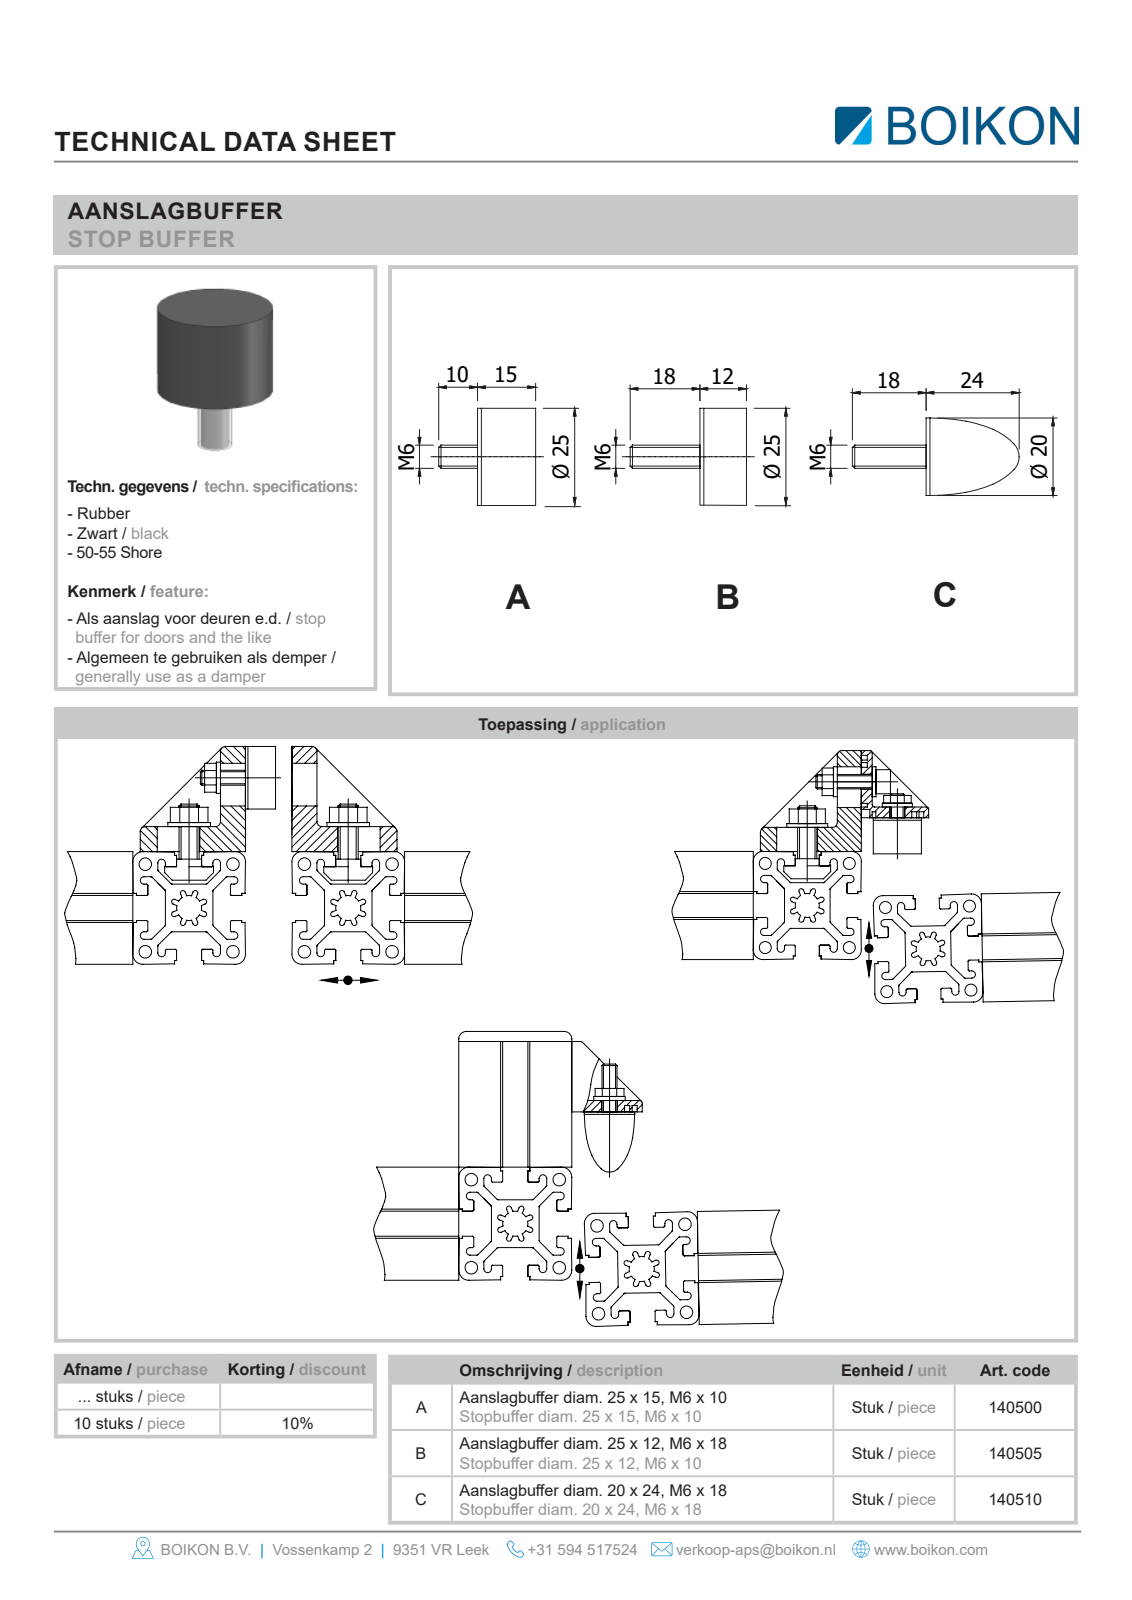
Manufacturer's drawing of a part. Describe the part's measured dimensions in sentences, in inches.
The part is named "Root; 140505Aanslagbuffer diam 25x12, M6x18BOIKON". Its 3-D file was written by "HiCAD 2013 1802.4 Build 509 (AUTOMOTIVE_DESIGN)". It is 1 solid with 5 faces: 3 planar, 2 cylindrical and 0 other. Overall it measures 1.181 by 0.984 by 0.984 inches. Its volume is 0.379 cubic inches and its surface area 3.401 square inches. Round bosses or shafts: 1 of diameter 0.984, 1 of diameter 0.188. The main face-to-face distances are 0.472, 0.709, 1.181.
